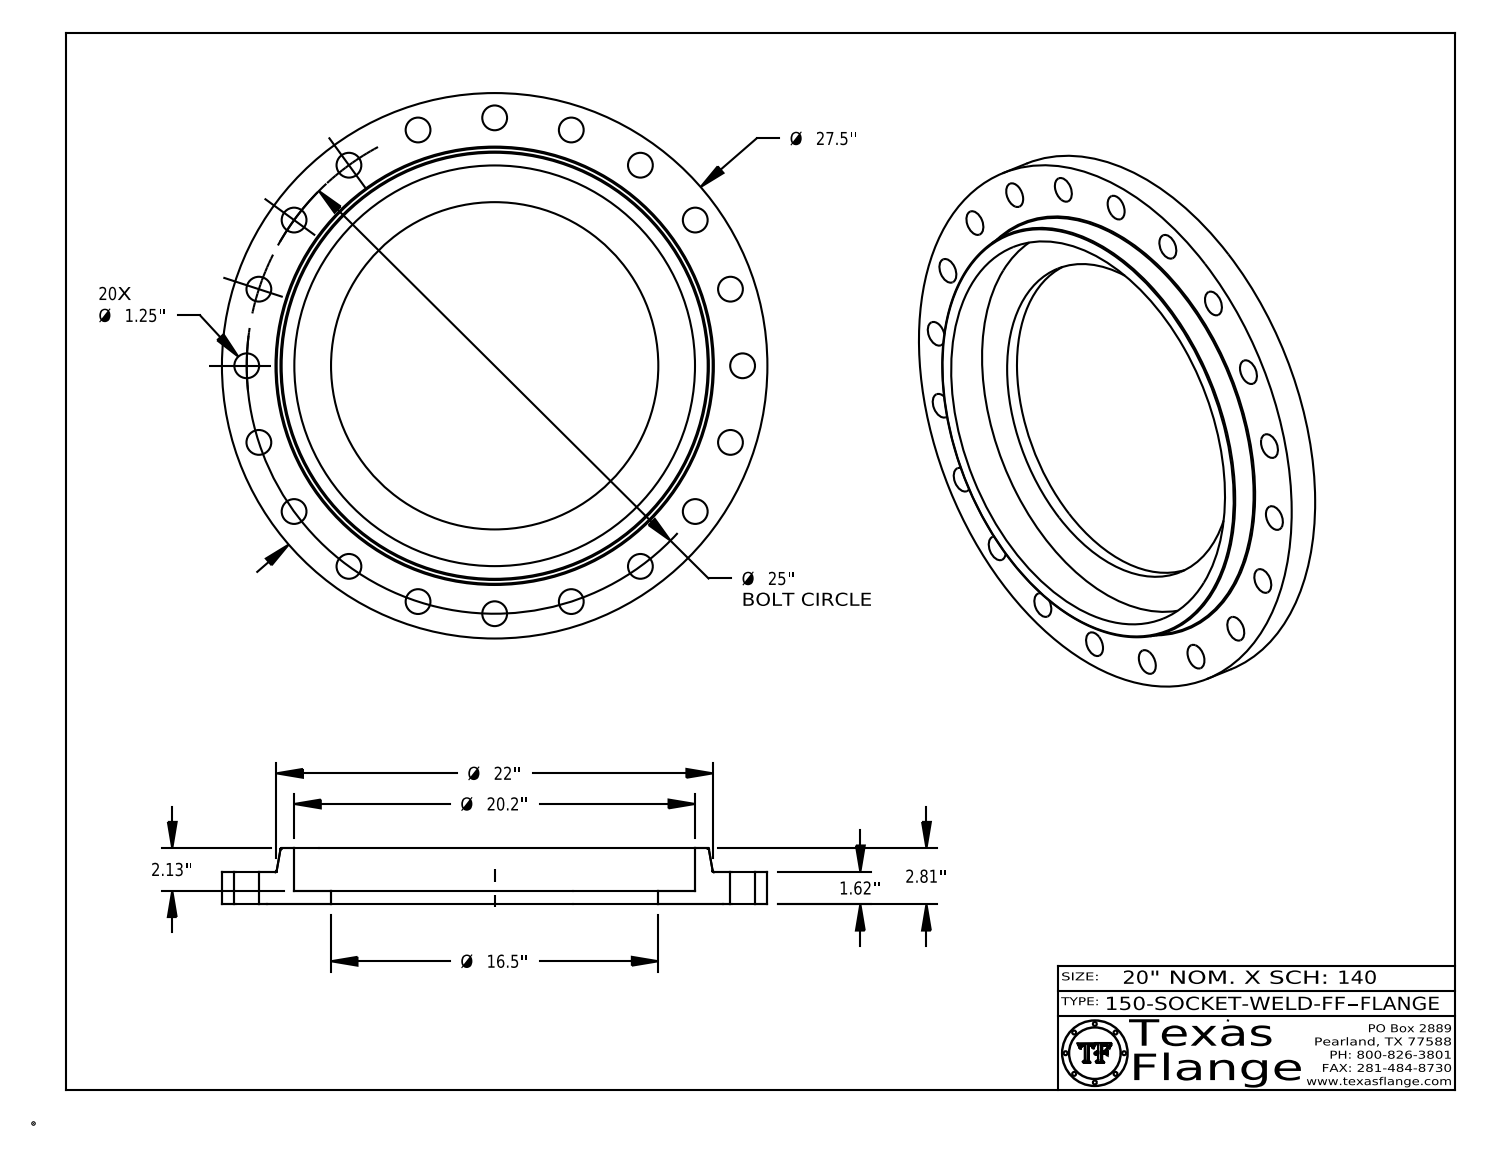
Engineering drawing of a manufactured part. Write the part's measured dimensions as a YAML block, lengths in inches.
part_name: "150-SOCKET-WELD-FF"
step_written_by: "CATIA V5 STEP AP214 (AUTOMOTIVE_DESIGN)"
units: inches
bodies: {solids: 1, faces: 442, planar: 370, cylindrical: 66, other: 6}
overall_size: [27.5, 27.5, 2.81]
volume: 538.2
surface_area: 1215
round_holes:
  - {diameter: 1.25, count: 20}
  - {diameter: 0.495, count: 1}
  - {diameter: 16.5, count: 1}
  - {diameter: 20.2, count: 1}
round_bosses_or_shafts:
  - {diameter: 0.03, count: 8}
  - {diameter: 27.5, count: 1}
  - {diameter: 0.39, count: 1}
face_to_face_distances: [1.62, 0.68, 0.94, 2.81, 2.13, 1.19, 1.605, 0.925, 0.015, 1.205]
hole_center_spacings: [12.5, 14.694, 17.678, 20.225, 23.776, 24.692, 11.35, 22.275]
